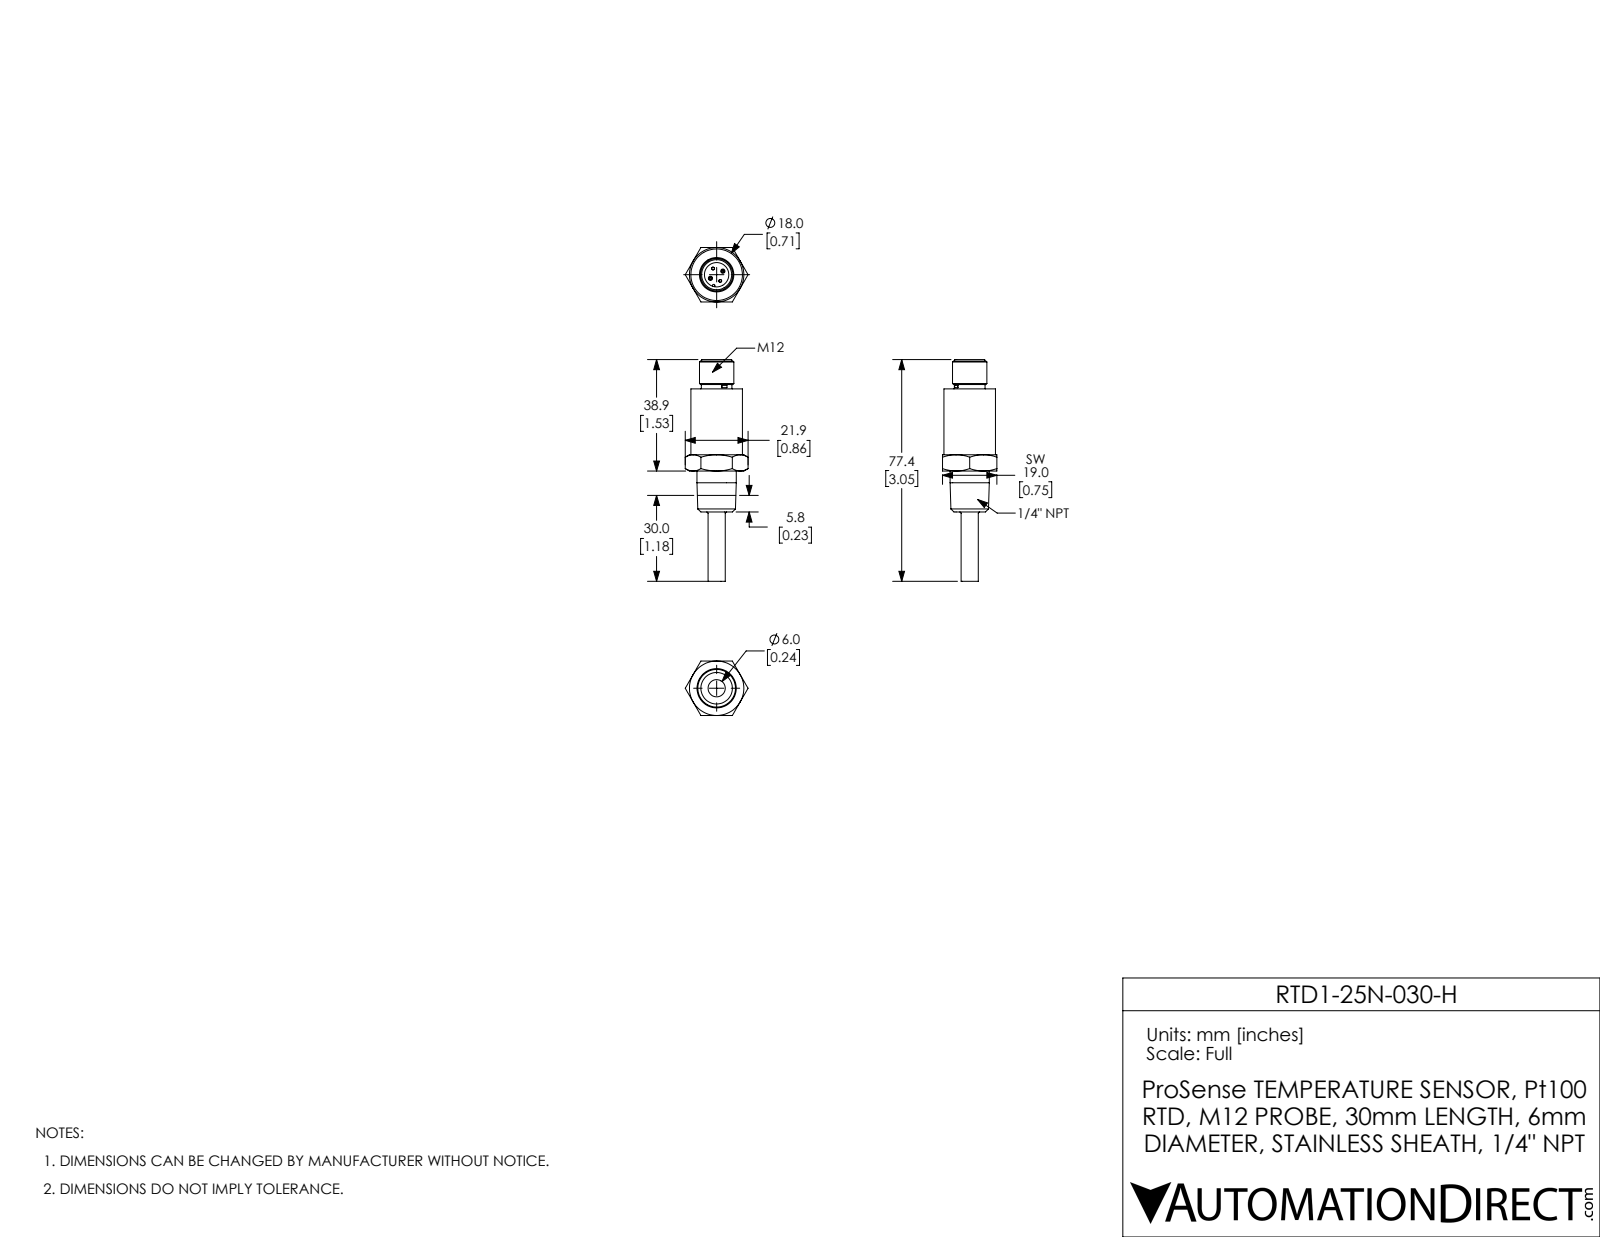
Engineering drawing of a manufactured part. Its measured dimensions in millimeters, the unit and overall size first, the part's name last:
Units: millimetres
Overall size (bounding box): 77.4 × 21.9 × 19
Round holes (diameter × count): ⌀8.5 ×1
Round bosses / shafts (diameter × count): ⌀1 ×4, ⌀18 ×1, ⌀13.7 ×1, ⌀12 ×1, ⌀10.7 ×1, ⌀10.5 ×1, ⌀6 ×1
Partial cylindrical surfaces — rounded edges, fillets, slot ends (radius × count): R0.4 ×1
Main face-to-face distances: 19, 28.7, 44.2, 24.2, 14.3, 43, 29.9, 1.2, 53.2, 38.9
Volume: 10 900 mm³ · Surface area: 3 993 mm²
Bodies: 1 solid, 95 faces (32 planar, 23 cylindrical, 40 other)
Part name (STEP PRODUCT): RTD1-25N-030-H
STEP written by: SolidWorks 2017 (AUTOMOTIVE_DESIGN)
